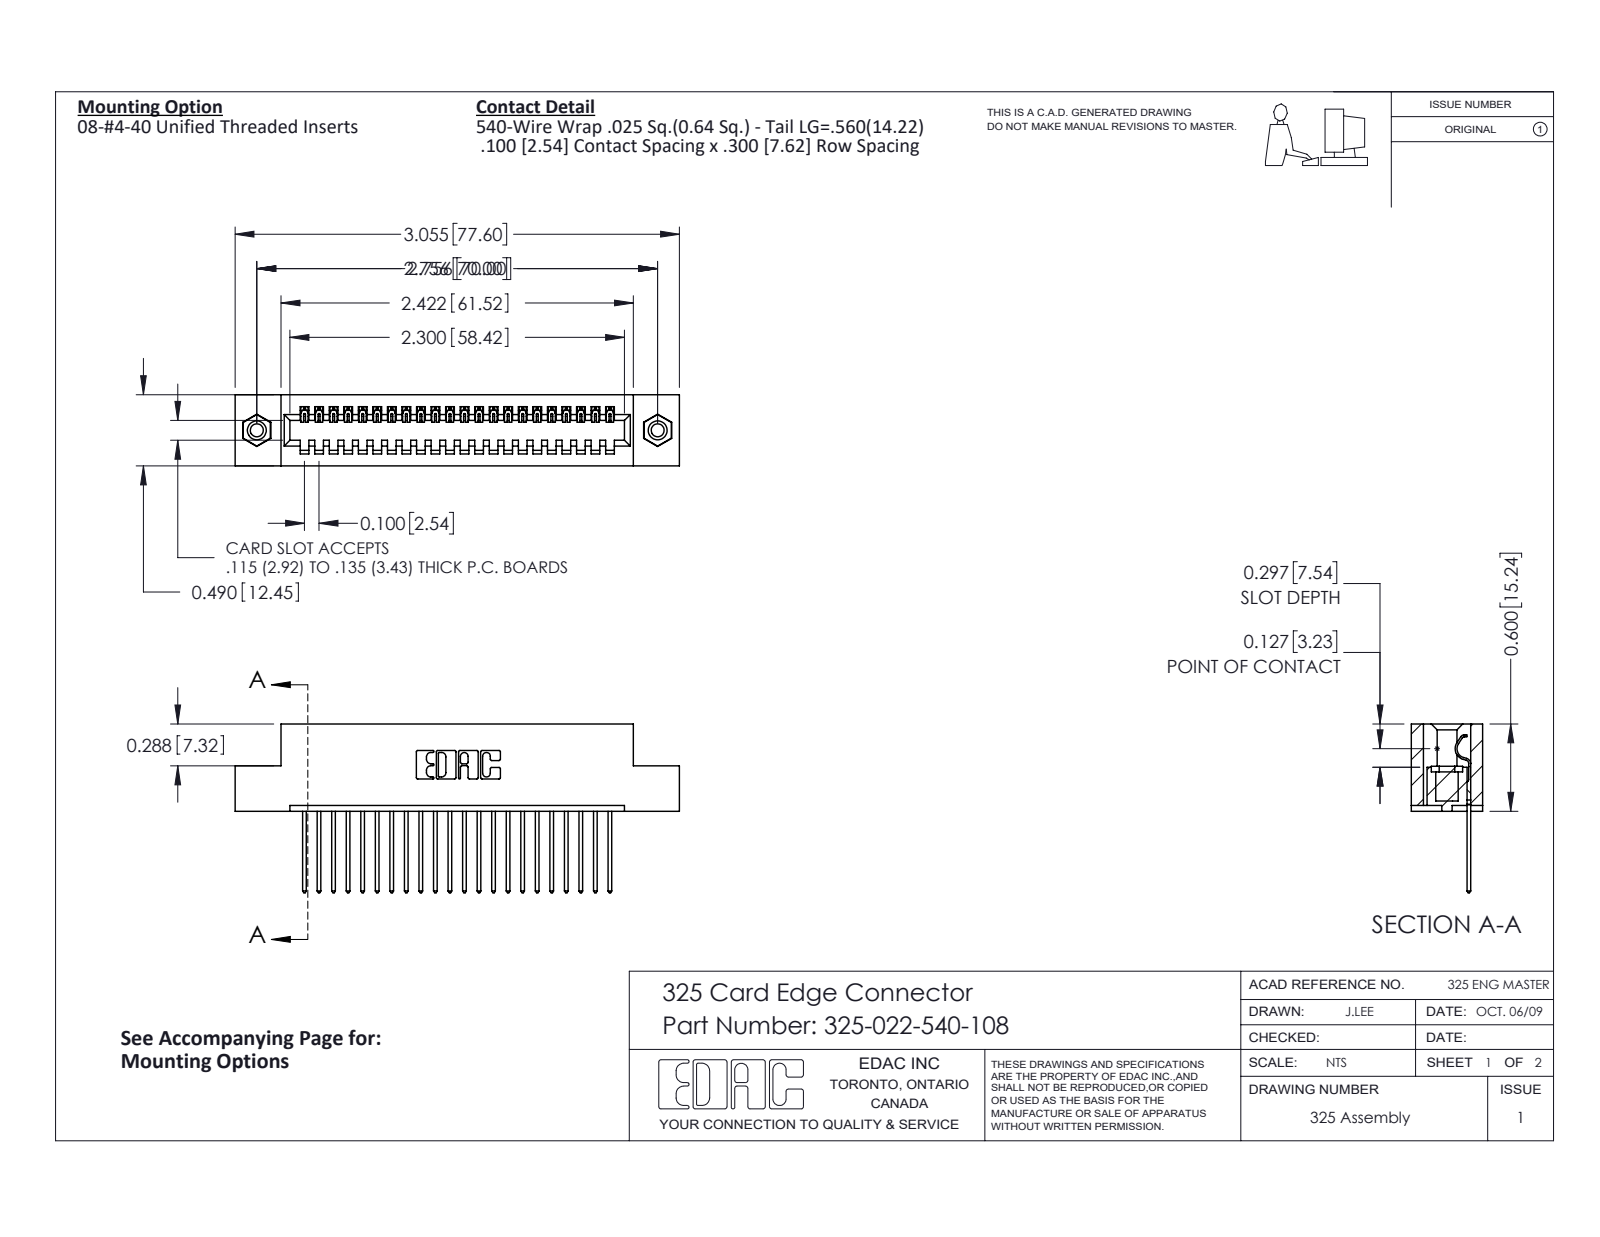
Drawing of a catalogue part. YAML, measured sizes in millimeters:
part_name: "325-022-540-108; 325-292-001_325-293-140; 345-250-001_345-250-003-102; 325 Part_TI"
step_written_by: "SolidWorks 2016 (CONFIG_CONTROL_DESIGN)"
units: millimeters
bodies: {solids: 25, faces: 1450, planar: 1026, cylindrical: 408, other: 16}
overall_size: [77.6, 29.5, 12.4]
volume: 9720
surface_area: 10510
round_holes:
  - {diameter: 2.3, count: 2}
  - {diameter: 3.2, count: 2}
  - {diameter: 4.1, count: 2}
round_bosses_or_shafts:
  - {diameter: 3.9, count: 2}
partial_cylinders:
  - {radius: 0.2, count: 44}
  - {radius: 0.3, count: 44}
  - {radius: 0.3, count: 22}
  - {radius: 0.2, count: 6}
  - {radius: 0.8, count: 6}
  - {radius: 0.7, count: 3}
  - {radius: 0.4, count: 1}
  - {radius: 0.6, count: 1}
face_to_face_distances: [2.1, 10.3, 7.6, 12.4, 2.7, 9.7, 0.6, 1, 8.3, 2.5]
hole_center_spacings: [70]
